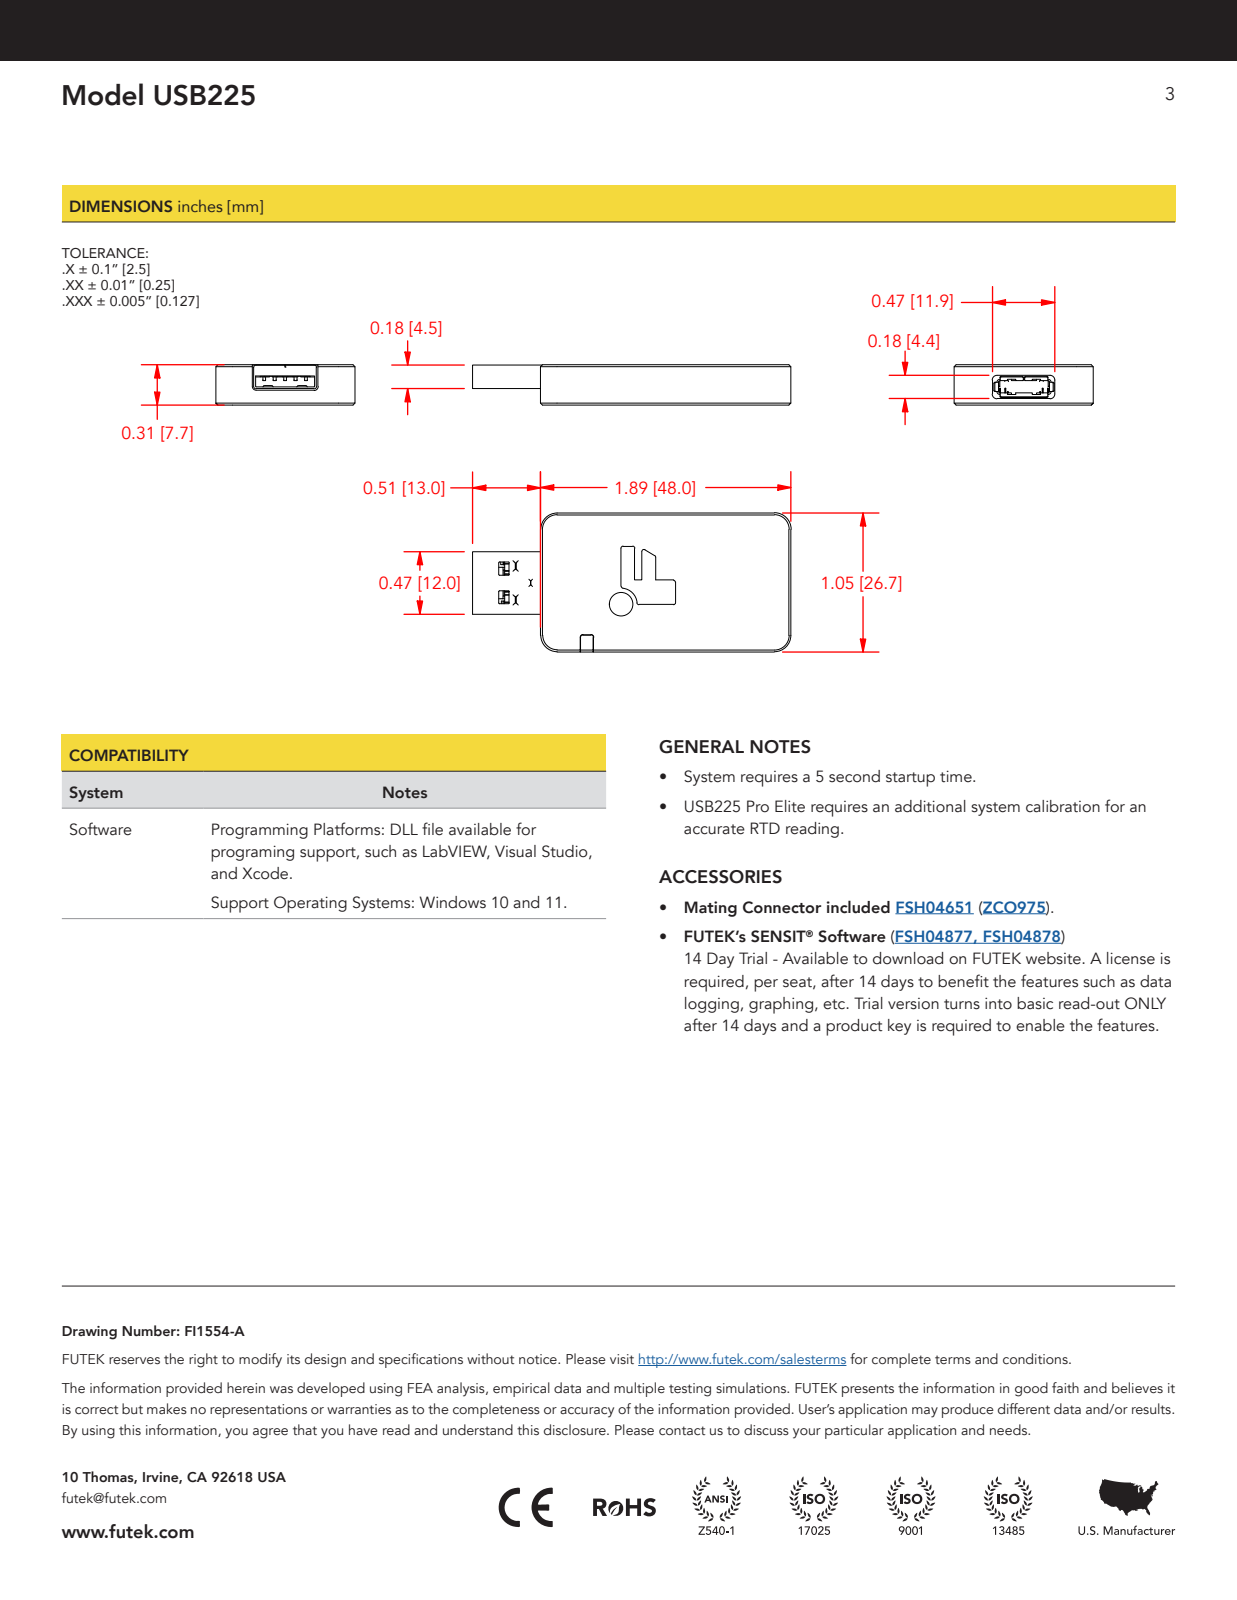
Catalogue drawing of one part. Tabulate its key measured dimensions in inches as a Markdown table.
| quantity | value |
| --- | --- |
| part name | USB225 |
| STEP written by | Autodesk Inventor 2020 (AUTOMOTIVE_DESIGN) |
| units | inches |
| bodies | 1 solid, 1162 faces (835 planar, 299 cylindrical, 28 other) |
| overall size | 2.403 × 1.05 × 0.305 |
| volume | 0.611 in³ |
| surface area | 8.25 in² |
| round holes (diameter × count) | 0.178 × 1 |
| partial cylindrical surfaces (radius × count) | 0.014 × 16, 0.008 × 15, 0.012 × 13, 0.004 × 12, 0.006 × 10, 0.015 × 10, 0.016 × 5, 0.018 × 4 |
| main face-to-face distances | 0.303, 1.05, 0.126, 0.303, 0.177, 0.026, 0.014, 0.178, 0.015, 0.288 |
